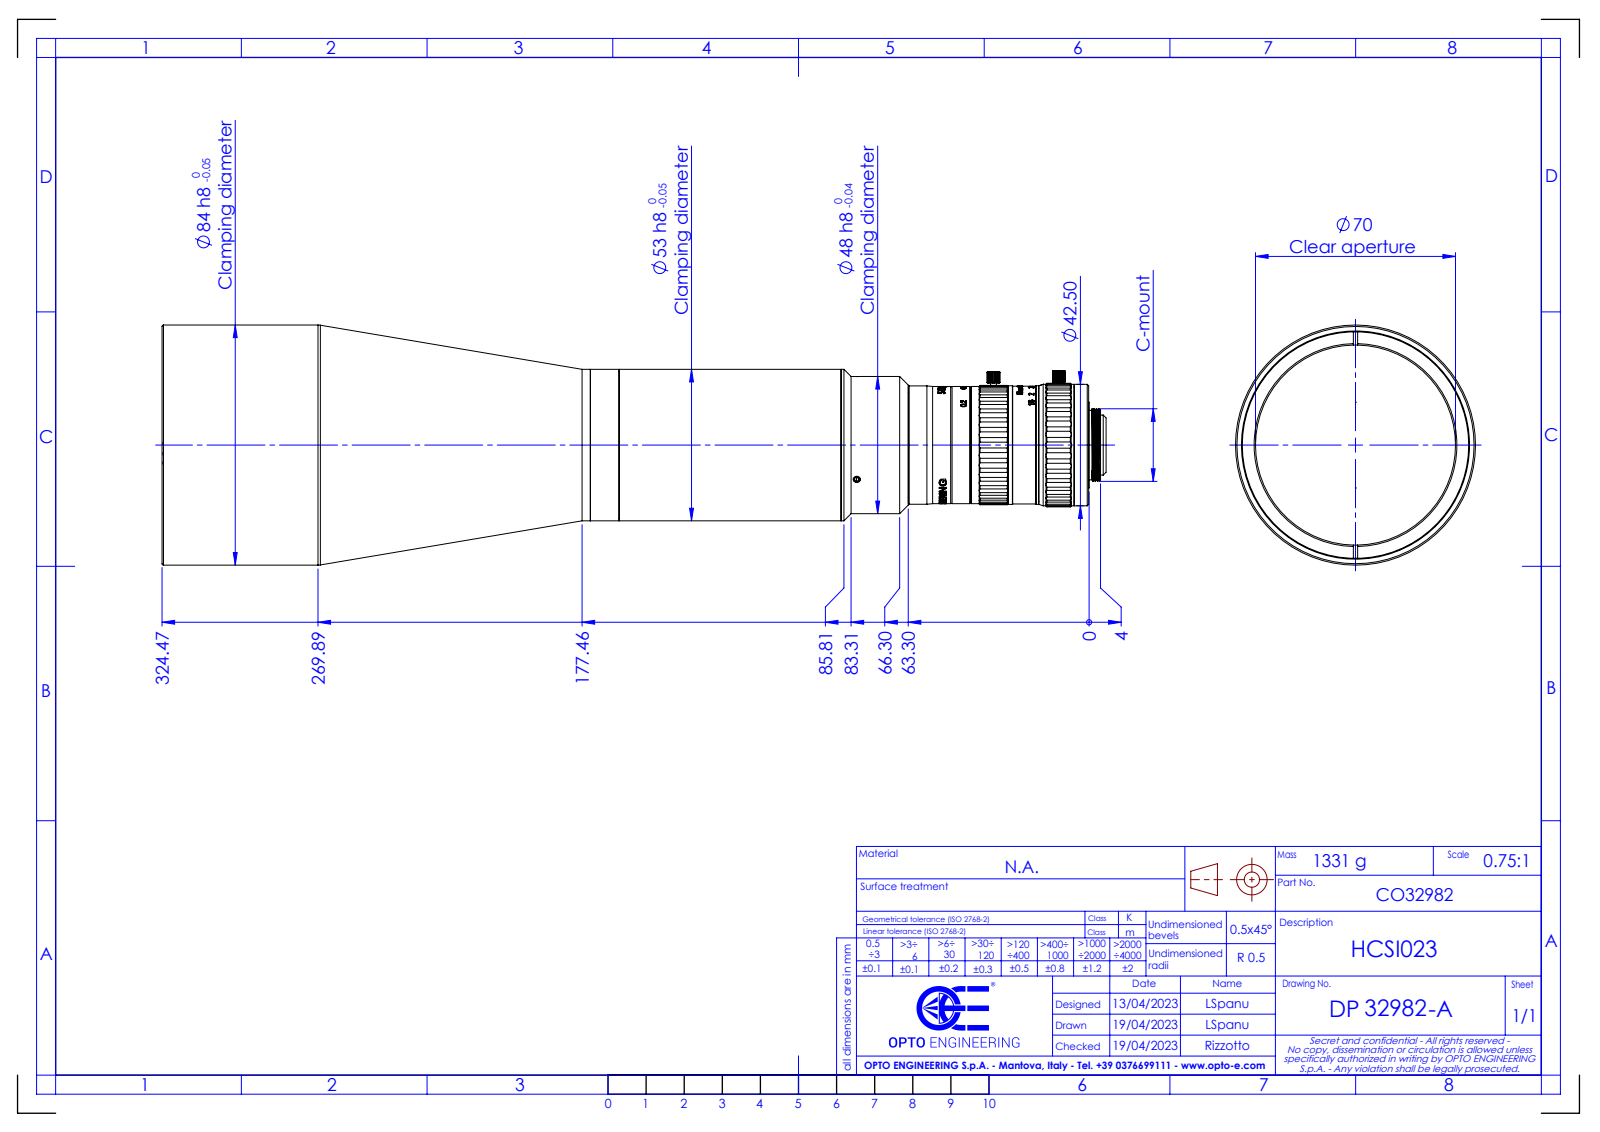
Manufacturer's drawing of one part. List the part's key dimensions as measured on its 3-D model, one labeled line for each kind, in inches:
Part name (STEP PRODUCT): DP32982-A_HCSI023
STEP written by: SolidWorks 2021 (CONFIG_CONTROL_DESIGN)
Units: inches
Bodies: 0 solids, 674 faces (100 planar, 366 cylindrical, 208 other)
Overall size (bounding box): 13.008 × 3.307 × 3.307
Round holes (diameter × count): ⌀0.098 ×3, ⌀0.496 ×1, ⌀1.189 ×1, ⌀2.756 ×1, ⌀3.12 ×1
Round bosses / shafts (diameter × count): ⌀3.307 ×1, ⌀2.087 ×1, ⌀1.89 ×1, ⌀1.673 ×1, ⌀1.634 ×1, ⌀1.63 ×1, ⌀1.622 ×1, ⌀1.614 ×1
Partial cylindrical surfaces — rounded edges, fillets, slot ends (radius × count): R0.079 ×72, R0.051 ×3, R0.089 ×2, R0.805 ×1, R0.809 ×1, R0.823 ×1, R0.852 ×1
Main face-to-face distances: 0.108, 9.337, 9.228, 12.748, 12.64, 3.412, 6.28, 6.171, 3.057, 6.469
